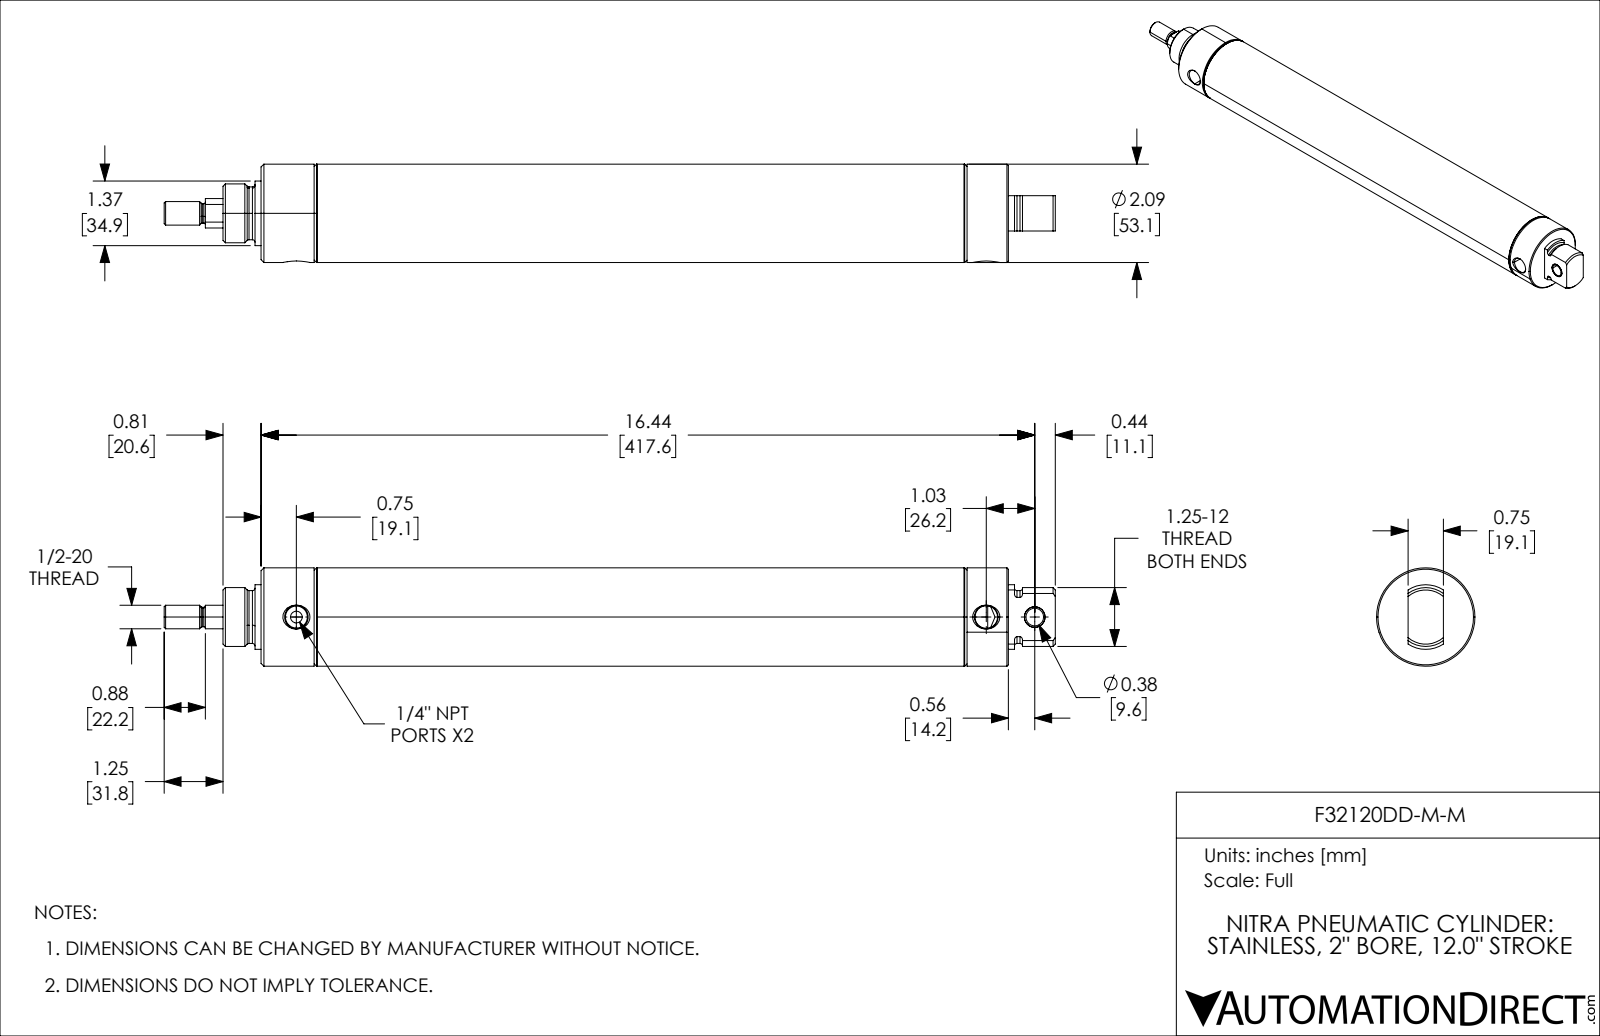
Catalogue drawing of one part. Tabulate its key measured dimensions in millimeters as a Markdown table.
| quantity | value |
| --- | --- |
| part name | F32120DD-M_11; F32120DD-M-M; F32120DD-M_3; F32120DD-M_7 (+2 more) |
| STEP written by | SolidWorks 2021 (CONFIG_CONTROL_DESIGN) |
| units | millimeters |
| bodies | 5 solids, 160 faces (31 planar, 60 cylindrical, 69 other) |
| overall size | 481.02 × 53.09 × 53.09 |
| volume | 344 263 mm³ |
| surface area | 177 071 mm² |
| round holes (diameter × count) | 6.35 × 1, 9.55 × 1, 11.15 × 1, 12.18 × 1, 16.52 × 1, 19.05 × 1, 49.05 × 1 |
| round bosses / shafts (diameter × count) | 53.09 × 1, 51.16 × 1, 34.87 × 1, 31.75 × 1, 28.51 × 1, 15.88 × 1, 12.7 × 1, 11.15 × 1 |
| partial cylindrical surfaces (radius × count) | 14.25 × 1 |
| main face-to-face distances | 30.17, 304.8, 334.97, 365.2, 60.4, 30.23, 334.98, 30.18, 30.22, 38.15 |
| hole center spacings | 26.16, 26.17, 372.36, 398.52, 398.53 |
